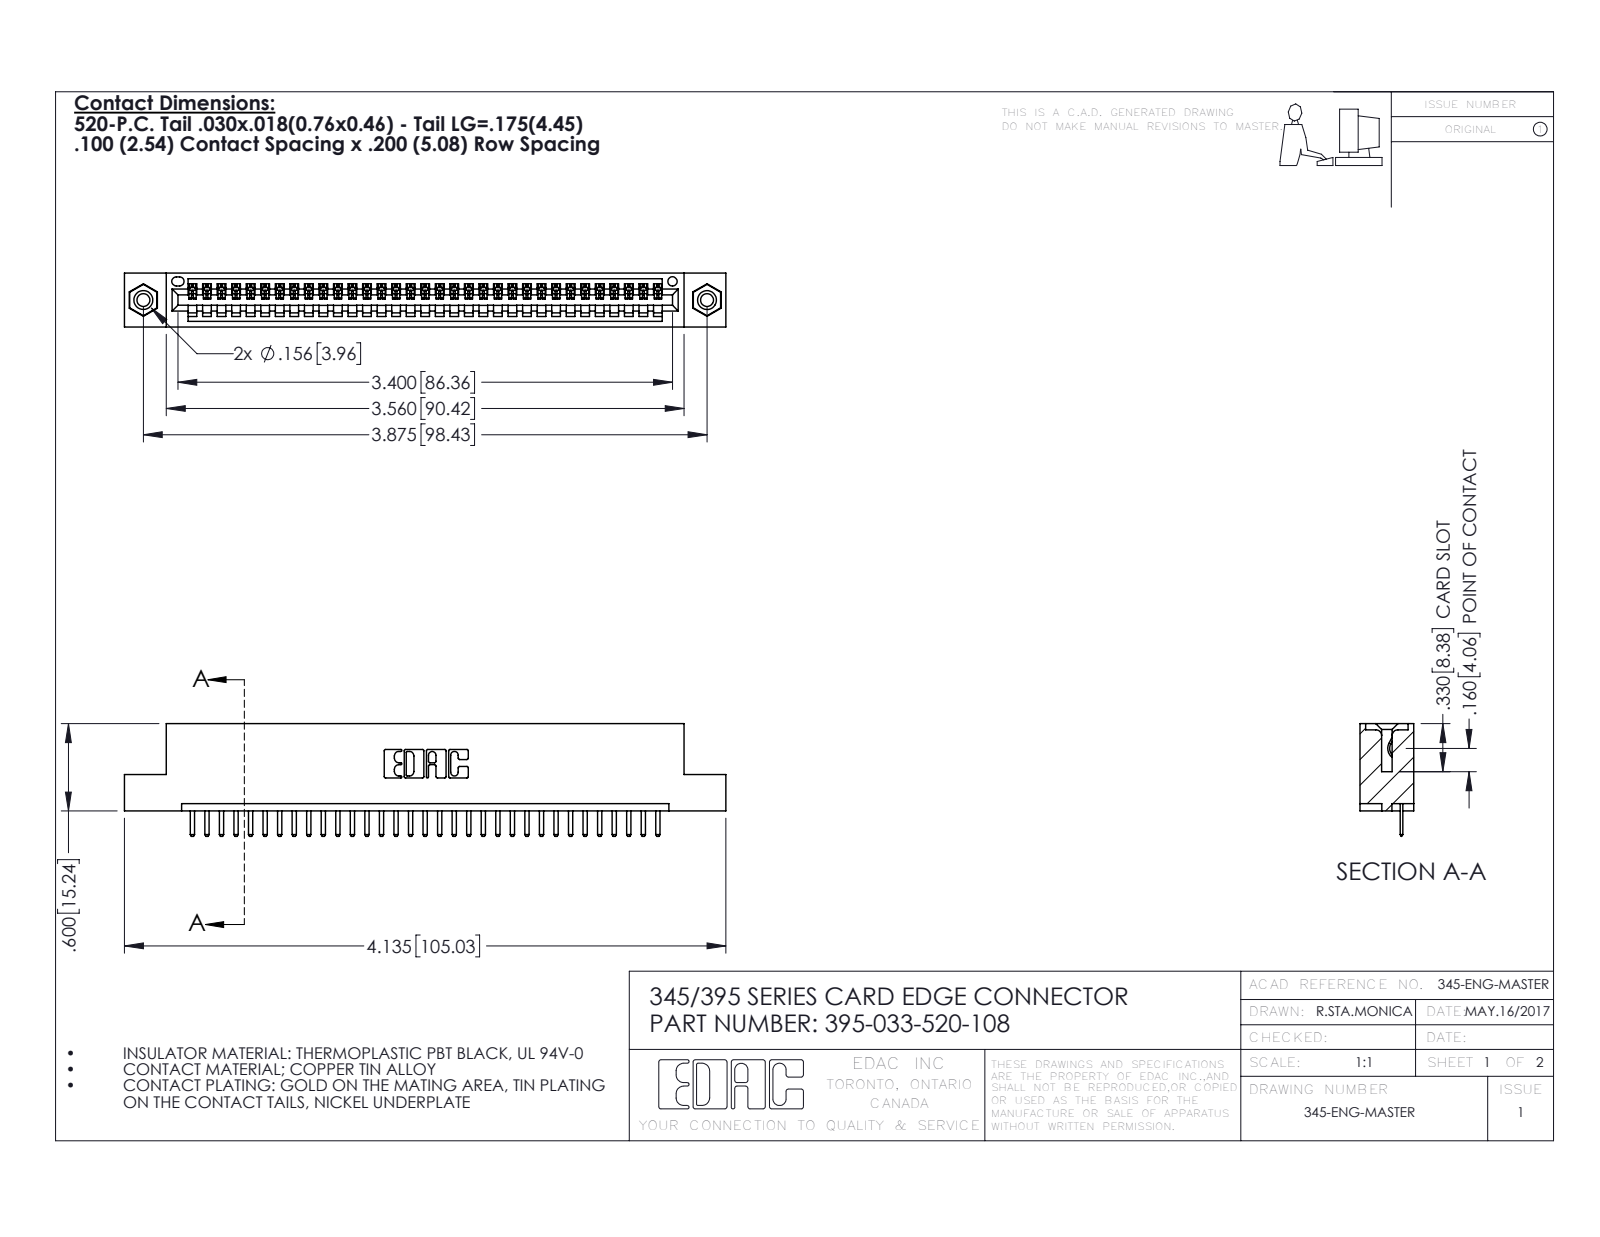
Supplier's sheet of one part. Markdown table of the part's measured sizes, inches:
| quantity | value |
| --- | --- |
| part name | 345-250-001_345-250-003-102; 395-033-520-108; 345 Part_Flush Mounting Lugs - 0.156 Dia-TI; 345-292-001_345-293-120 |
| STEP written by | SolidWorks 2016 (CONFIG_CONTROL_DESIGN) |
| units | inches |
| bodies | 36 solids, 2232 faces (1498 planar, 718 cylindrical, 16 other) |
| overall size | 4.135 × 0.775 × 0.37 |
| volume | 0.598 in³ |
| surface area | 19.55 in² |
| round holes (diameter × count) | 0.089 × 2, 0.125 × 2, 0.156 × 2, 0.064 × 1 |
| round bosses / shafts (diameter × count) | 0.155 × 2 |
| partial cylindrical surfaces (radius × count) | 0.01 × 68, 0.006 × 66, 0.01 × 22, 0.007 × 6, 0.031 × 6, 0.026 × 3, 0.031 × 2, 0.04 × 2 |
| main face-to-face distances | 0.072, 0.298, 0.37, 0.2, 0.098, 0.272, 0.025, 0.225, 0.072, 0.149 |
| hole center spacings | 0.27, 3.64, 3.875 |
